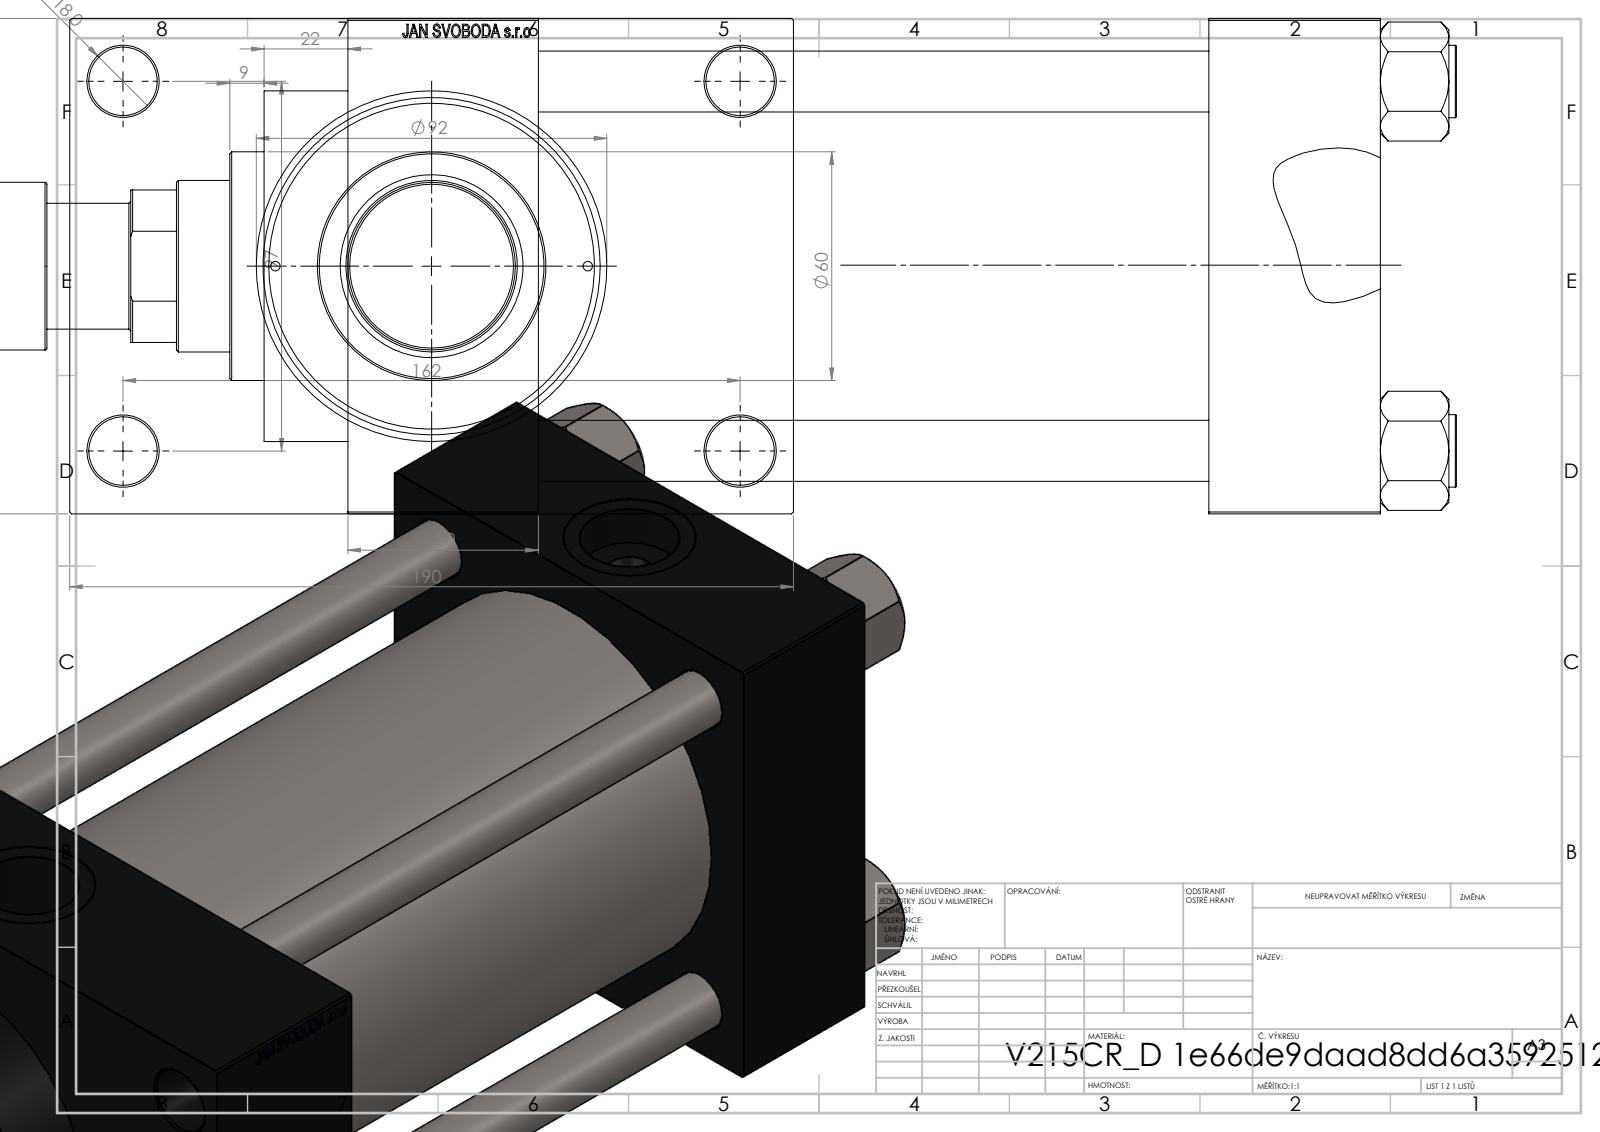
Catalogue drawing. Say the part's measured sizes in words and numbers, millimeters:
The part is named "V215CR_D_TYCINKA; V215CR_ROD_END_F; V215_VC_A; NUT_M5_D (+2 more)". Its 3-D file was written by "SolidWorks 2019 (CONFIG_CONTROL_DESIGN)". It is 12 solids with 1173 faces: 550 planar, 97 cylindrical and 526 other. Overall it measures 392 by 190 by 130 millimeters. Its volume is 3 012 000 cubic millimeters and its surface area 464 526 square millimeters. Round holes: 4 of diameter 16, 4 of diameter 18, 2 of diameter 2.5, 2 of diameter 7, 2 of diameter 26.44, 2 of diameter 35, 1 of diameter 31.5, 1 of diameter 45, 1 of diameter 48, 1 of diameter 76, 1 of diameter 85.5, 1 of diameter 100. Round bosses or shafts: 4 of diameter 19, 1 of diameter 106, 1 of diameter 92, 1 of diameter 60, 1 of diameter 44, 1 of diameter 33. The main face-to-face distances are 130, 45, 221, 176, 271, 226, 50, 30, 160, 190. The hole center spacings are 32.55, 49.02, 62.87, 68.52, 94.41, 96.9, 101.73, 102.27.
